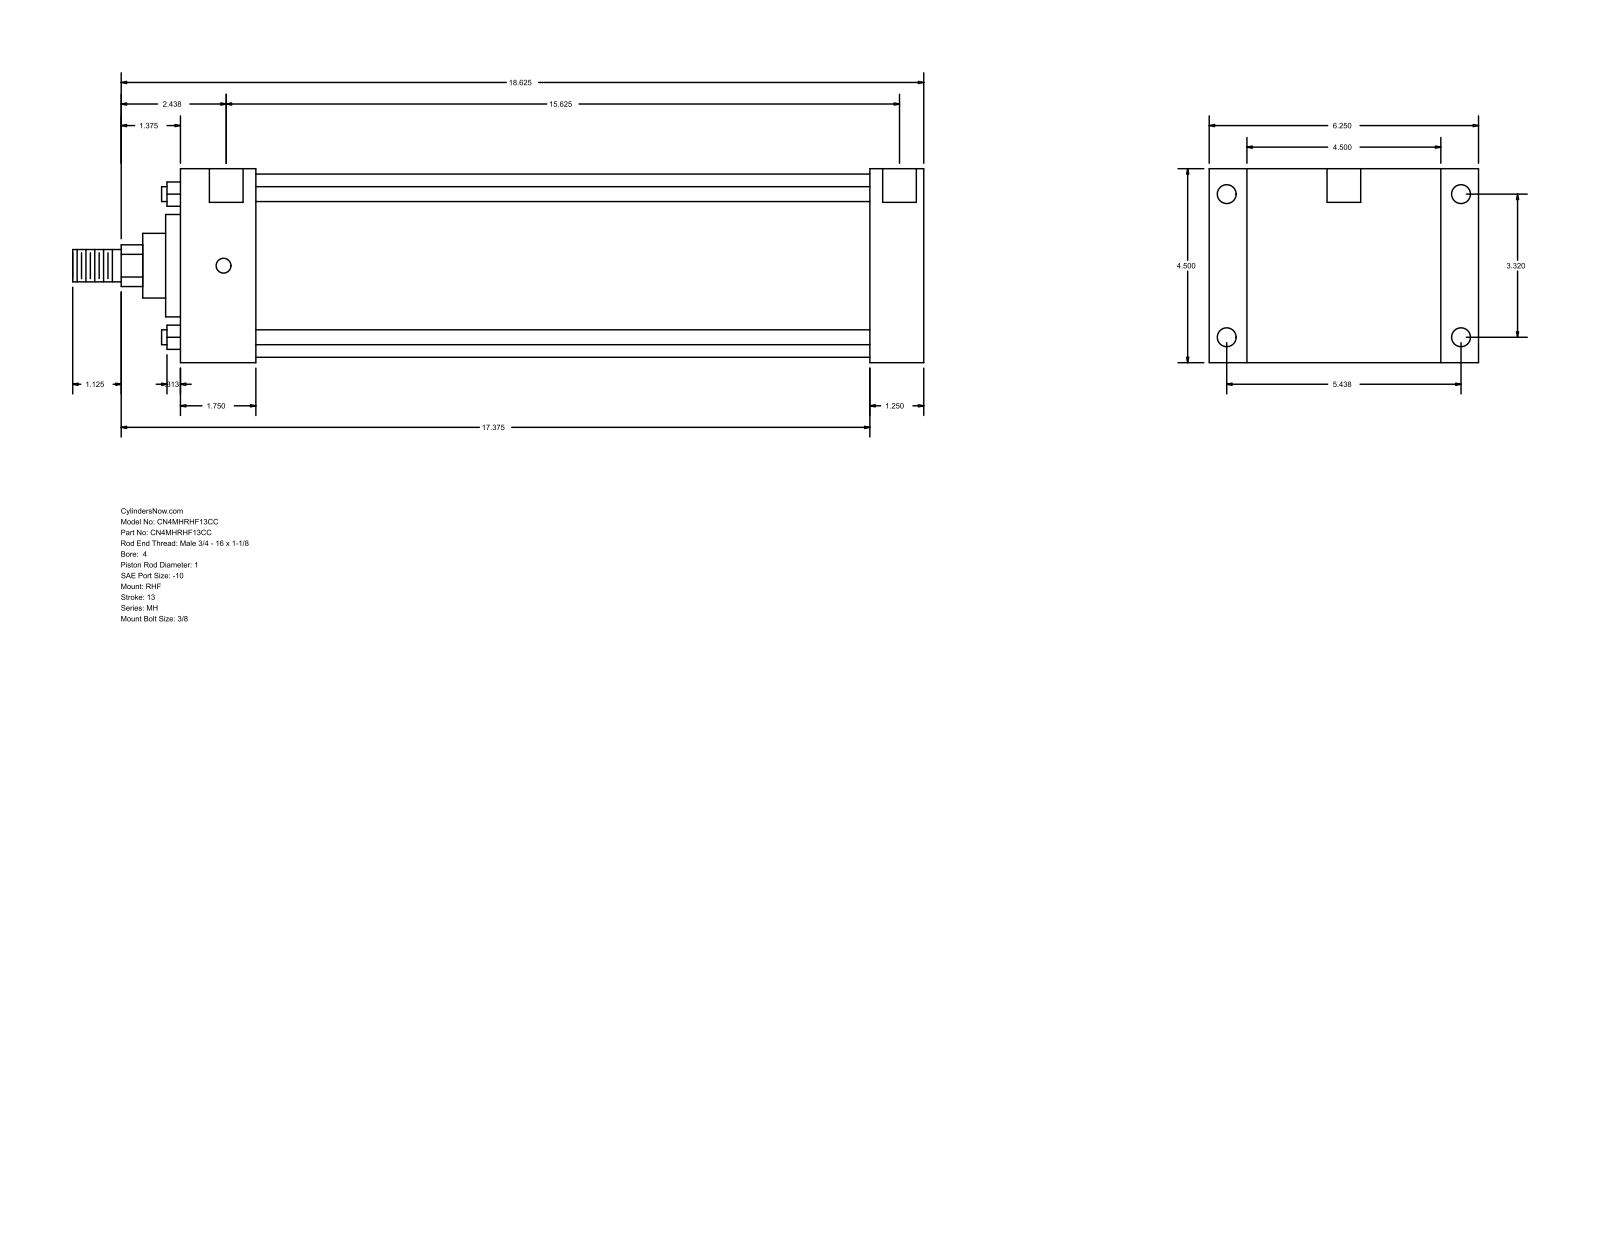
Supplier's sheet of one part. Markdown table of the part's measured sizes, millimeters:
| quantity | value |
| --- | --- |
| part name | MH_RHF__0400_1 |
| STEP written by | GSSL Pune (CONFIG_CONTROL_DESIGN) |
| units | millimeters |
| bodies | 0 solids, 90 faces (61 planar, 29 cylindrical, 0 other) |
| overall size | 501.65 × 158.75 × 114.3 |
| round holes (diameter × count) | 8.73 × 4, 11.13 × 4, 19.84 × 2 |
| round bosses / shafts (diameter × count) | 8.76 × 4, 107.95 × 1, 60.33 × 1, 38.1 × 1, 25.4 × 1, 19.05 × 1 |
| partial cylindrical surfaces (radius × count) | 12.29 × 1 |
| main face-to-face distances | 114.3, 438.15, 406.4, 31.75, 22.23, 136.53, 44.46, 361.94, 393.69, 158.76 |
| hole center spacings | 84.32, 138.12, 161.82, 400.05, 1.58, 1.59, 396.88, 398.46 |
